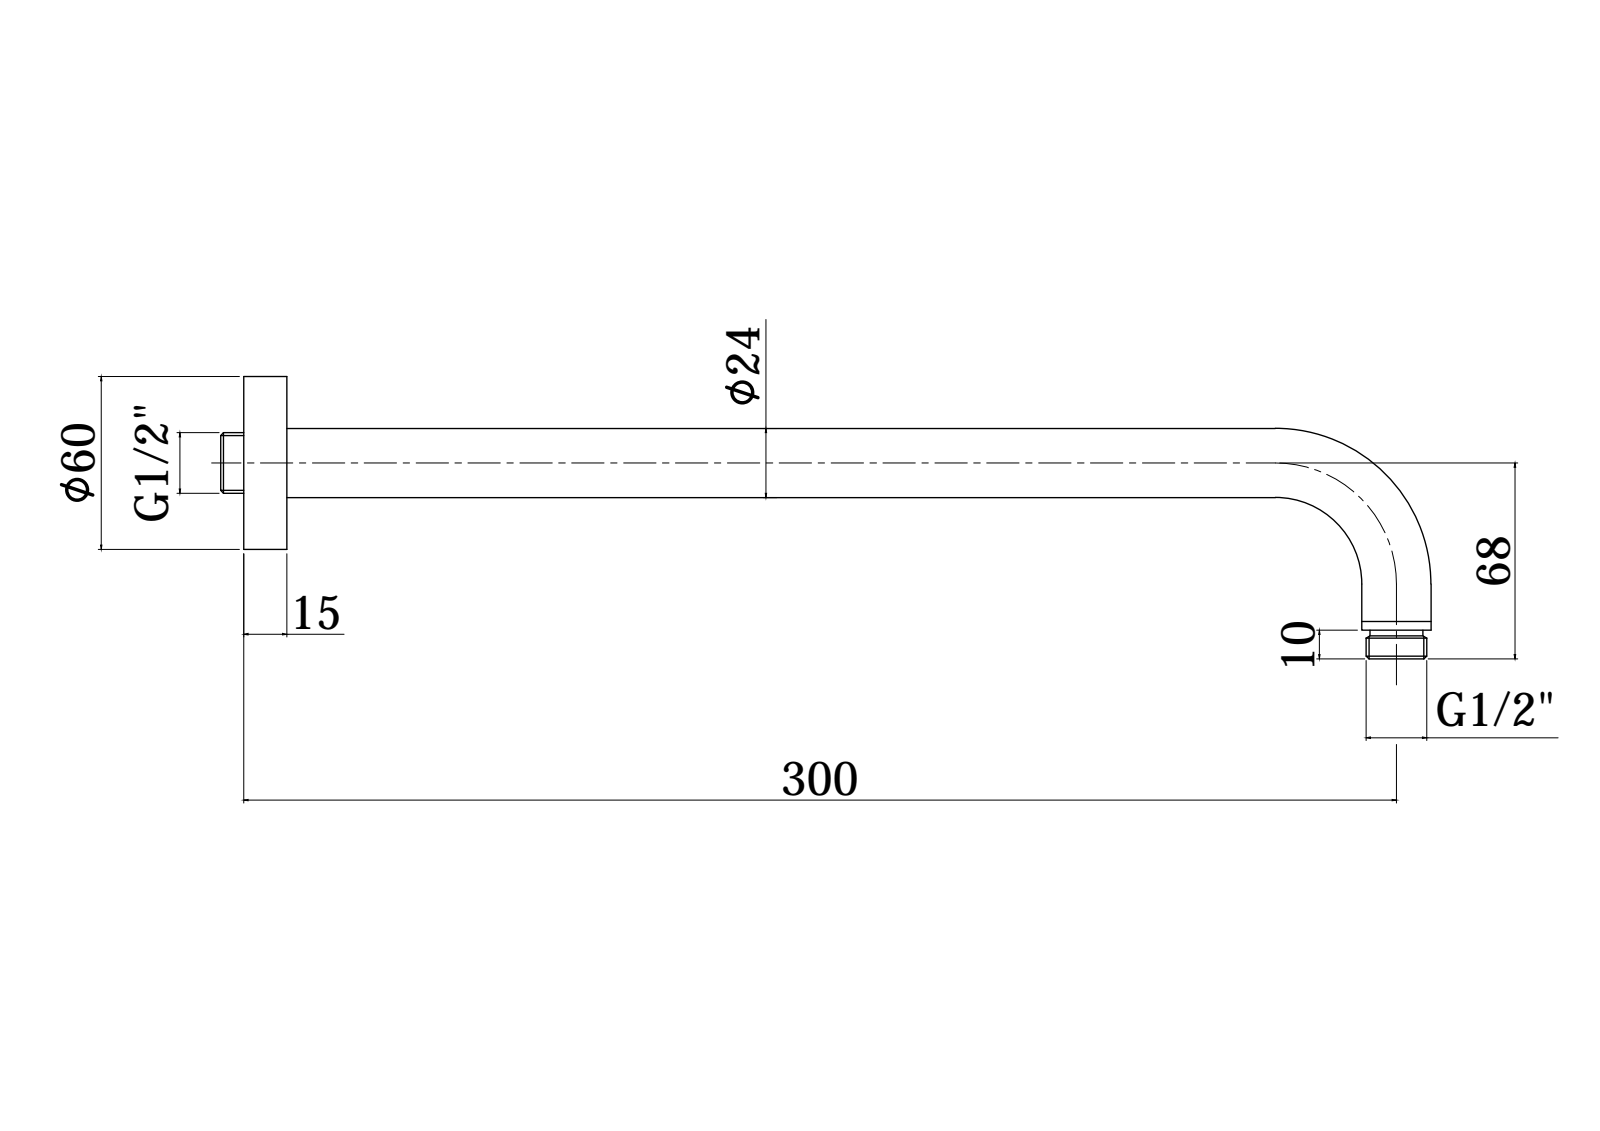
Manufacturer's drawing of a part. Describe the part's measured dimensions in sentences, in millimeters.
The part is named "ZSOF035CR". Its 3-D file was written by "CREO PARAMETRIC BY PTC INC, 2020044 (CONFIG_CONTROL_DESIGN)". It is 1 solid with 19 faces: 5 planar, 10 cylindrical and 4 other. Overall it measures 306 by 98 by 60 millimeters. Its volume is 190 487 cubic millimeters and its surface area 33 384 square millimeters. Round bosses or shafts: 2 of diameter 24, 1 of diameter 60, 1 of diameter 21, 1 of diameter 18.5. The main face-to-face distances are 15, 10, 8, 2.
